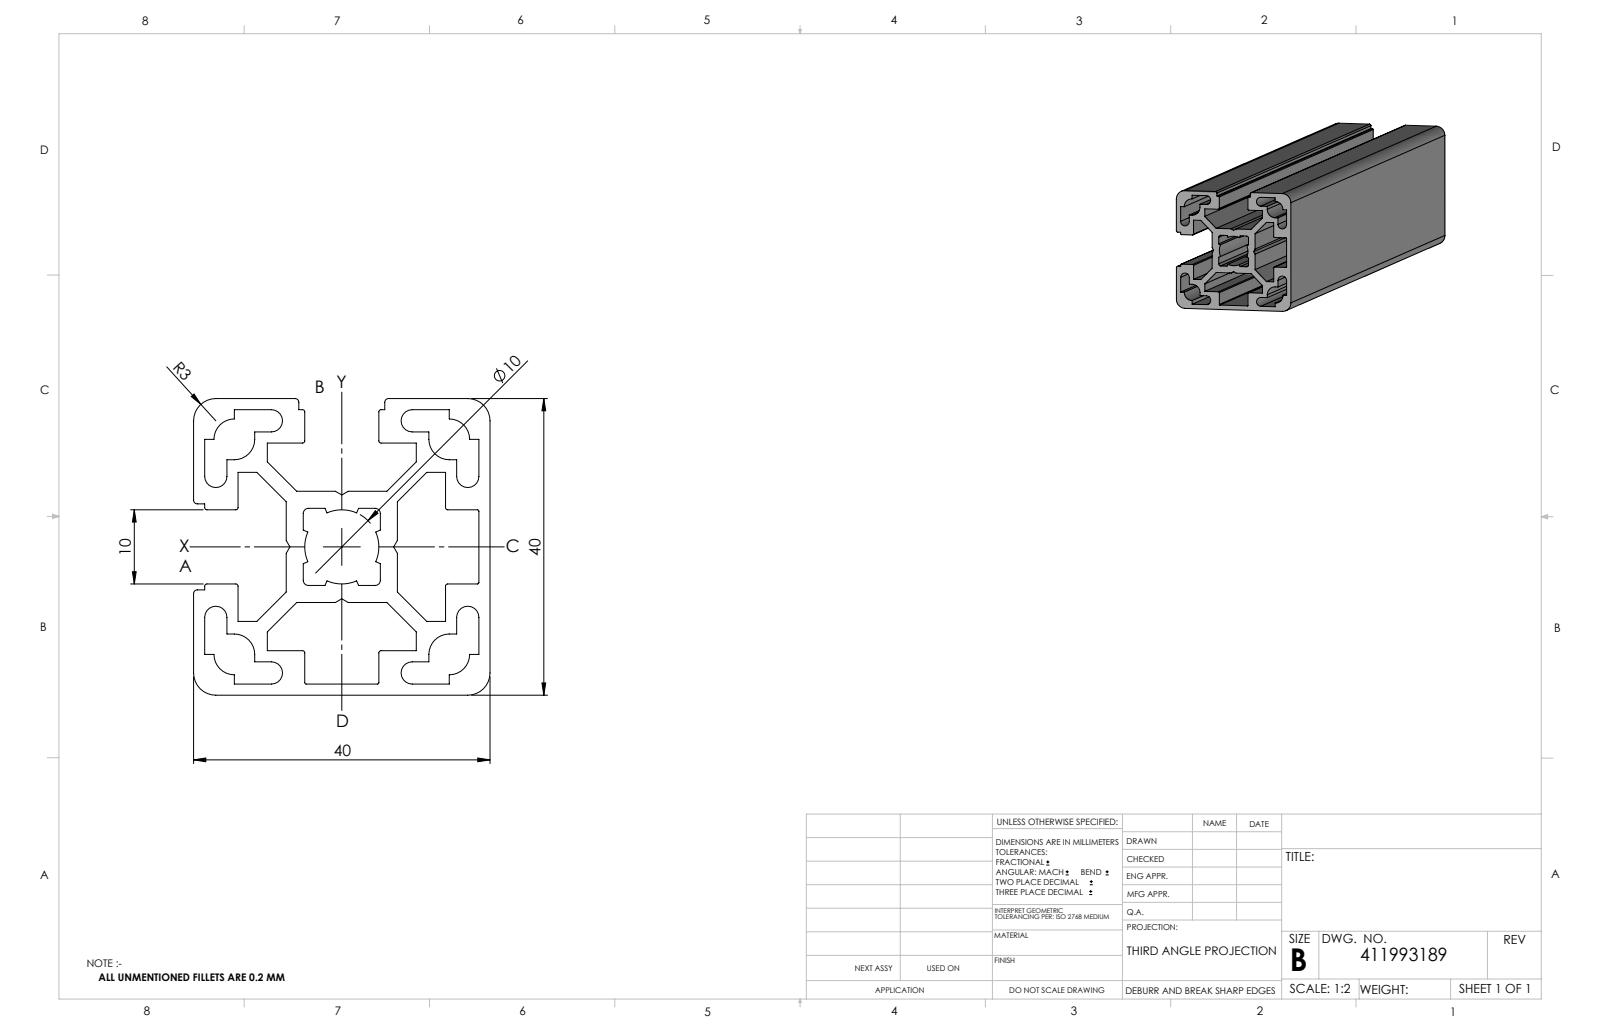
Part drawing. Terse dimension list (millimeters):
name: 411993189_c_1
written by: SolidWorks 2014 (CONFIG_CONTROL_DESIGN)
unit: mm
bodies: 1 solid, 165 faces (114 planar, 51 cylindrical, 0 other)
size: 200 × 40 × 40
volume: 119 219 mm³; area: 109 541 mm²
rounds: 12× R0.3, 8× R1.5, 4× R0.2, 4× R0.5, 4× R0.7, 4× R2.75, 4× R3, 1× R5
face distances: 1.5, 12.5, 38.5, 4.5, 34, 15, 40, 27.5, 11, 26
